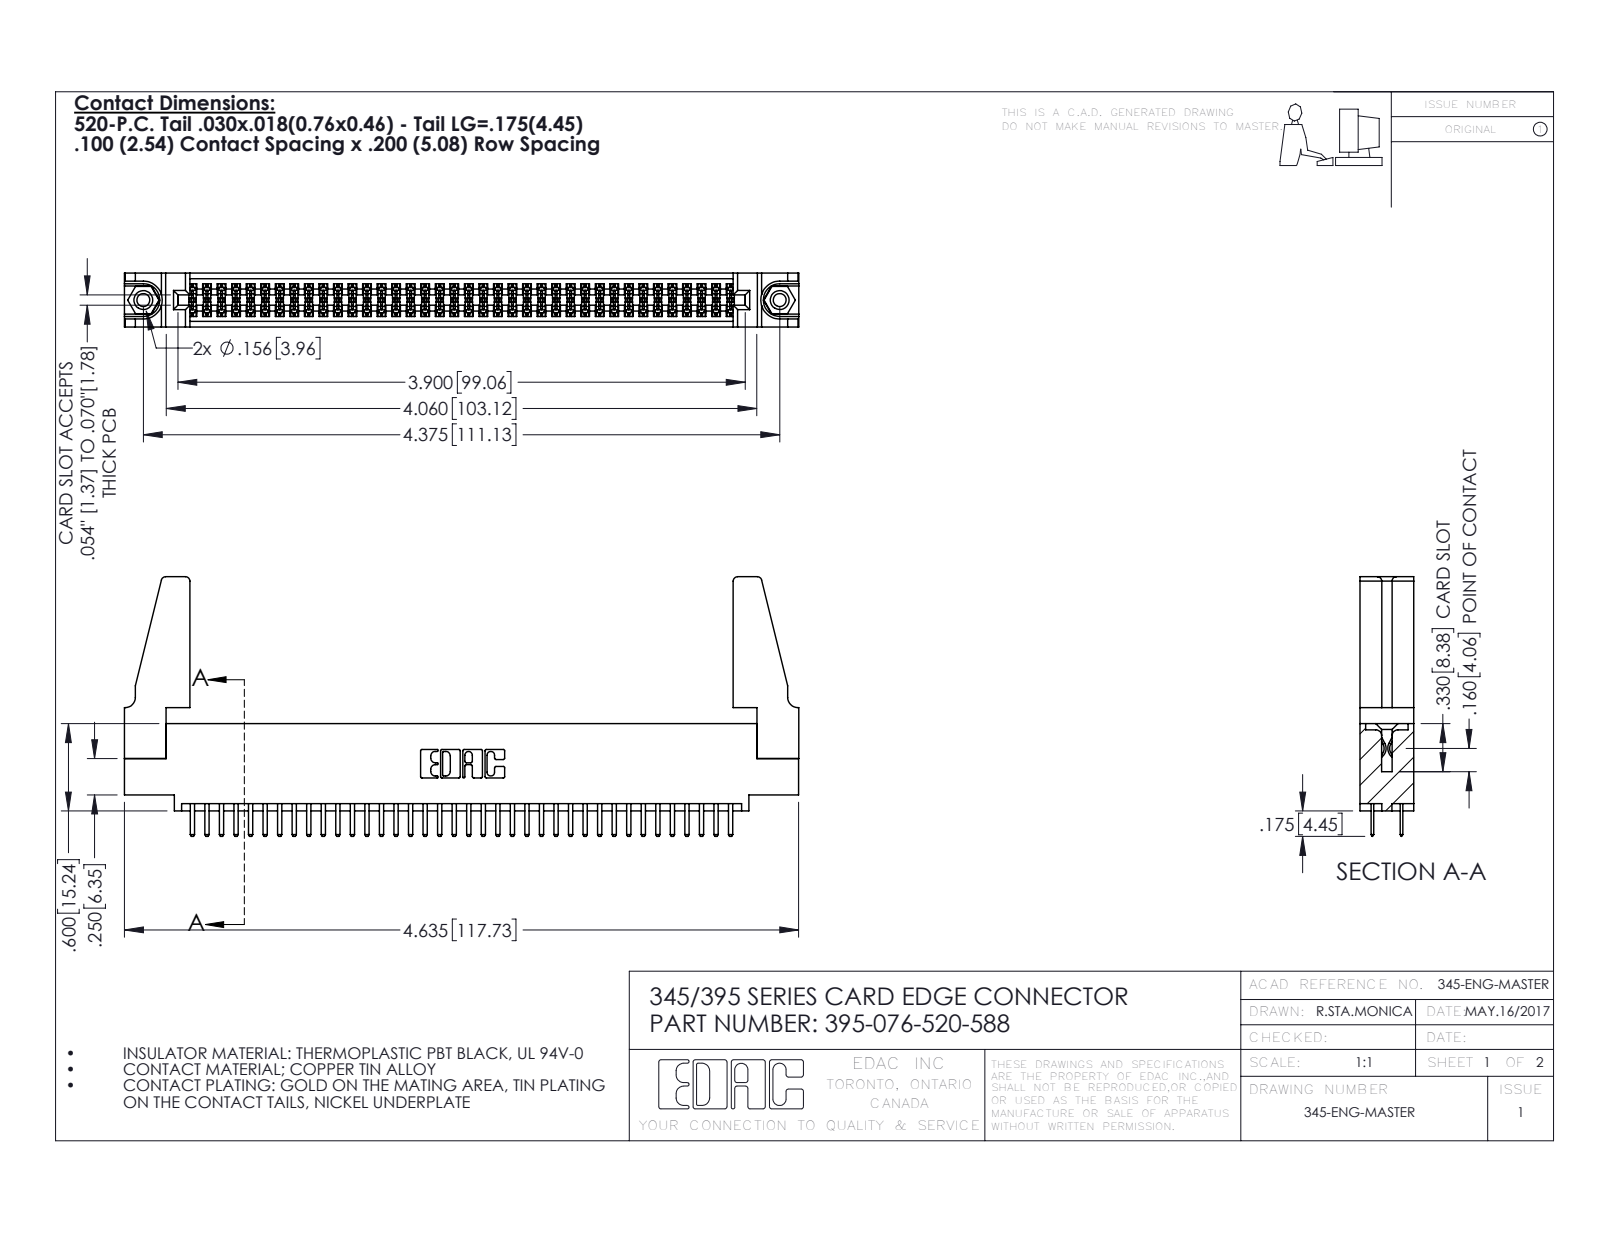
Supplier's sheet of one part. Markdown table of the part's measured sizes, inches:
| quantity | value |
| --- | --- |
| part name | 345-220-078_345-220-088; 395-076-520-588; 345 Part_0.110 Offset - 0.156 Dia-TH; 345-250-001_345-250-001-102 (+1 more) |
| STEP written by | SolidWorks 2016 (CONFIG_CONTROL_DESIGN) |
| units | inches |
| bodies | 81 solids, 4358 faces (2816 planar, 1526 cylindrical, 16 other) |
| overall size | 4.636 × 1.785 × 0.37 |
| volume | 0.888 in³ |
| surface area | 30.63 in² |
| round holes (diameter × count) | 0.089 × 2, 0.125 × 2, 0.156 × 2, 0.064 × 1 |
| round bosses / shafts (diameter × count) | 0.155 × 2 |
| partial cylindrical surfaces (radius × count) | 0.006 × 114, 0.01 × 80, 0.01 × 22, 0.03 × 8, 0.007 × 6, 0.031 × 6, 0.026 × 3, 0.014 × 2 |
| main face-to-face distances | 0.072, 0.298, 0.37, 0.2, 0.098, 0.272, 0.025, 0.225, 0.022, 0.072 |
| hole center spacings | 0.27, 4.139, 4.375 |
